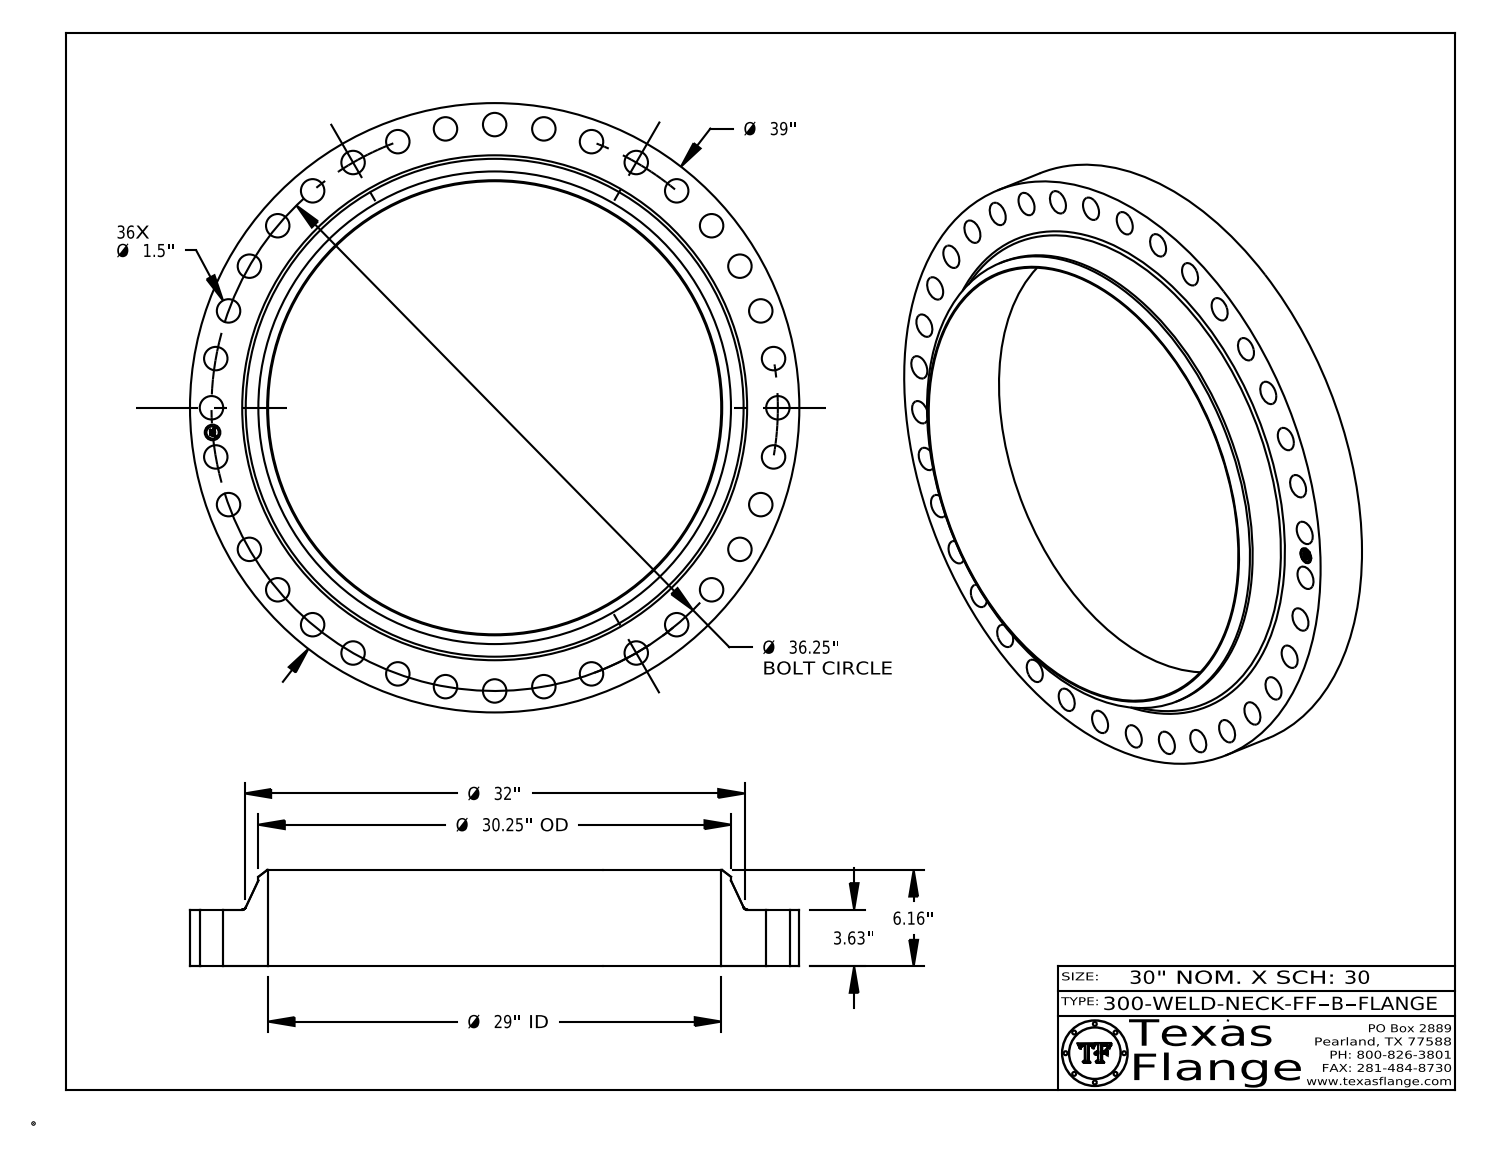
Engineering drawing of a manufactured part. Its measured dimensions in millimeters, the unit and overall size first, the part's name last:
Units: millimetres
Overall size (bounding box): 990.6 × 990.6 × 156.5
Round holes (diameter × count): ⌀38.1 ×36, ⌀25.4 ×1, ⌀736.6 ×1
Round bosses / shafts (diameter × count): ⌀1.5 ×8, ⌀990.6 ×1, ⌀768.4 ×1, ⌀20 ×1
Main face-to-face distances: 92.2, 156.5, 64.3, 91.8, 0.4, 64.6, 7.6, 7.4, 0.5, 1.4
Hole centre spacings: 460.4, 238.3, 705.3, 651.1, 906.8, 460.4, 917.2, 159.9
Volume: 31 510 000 mm³ · Surface area: 1 749 000 mm²
Bodies: 1 solid, 472 faces (368 planar, 98 cylindrical, 6 other)
Part name (STEP PRODUCT): 300-WELD-NECK-FF, Series B
STEP written by: CATIA V5 STEP AP214 (AUTOMOTIVE_DESIGN)
